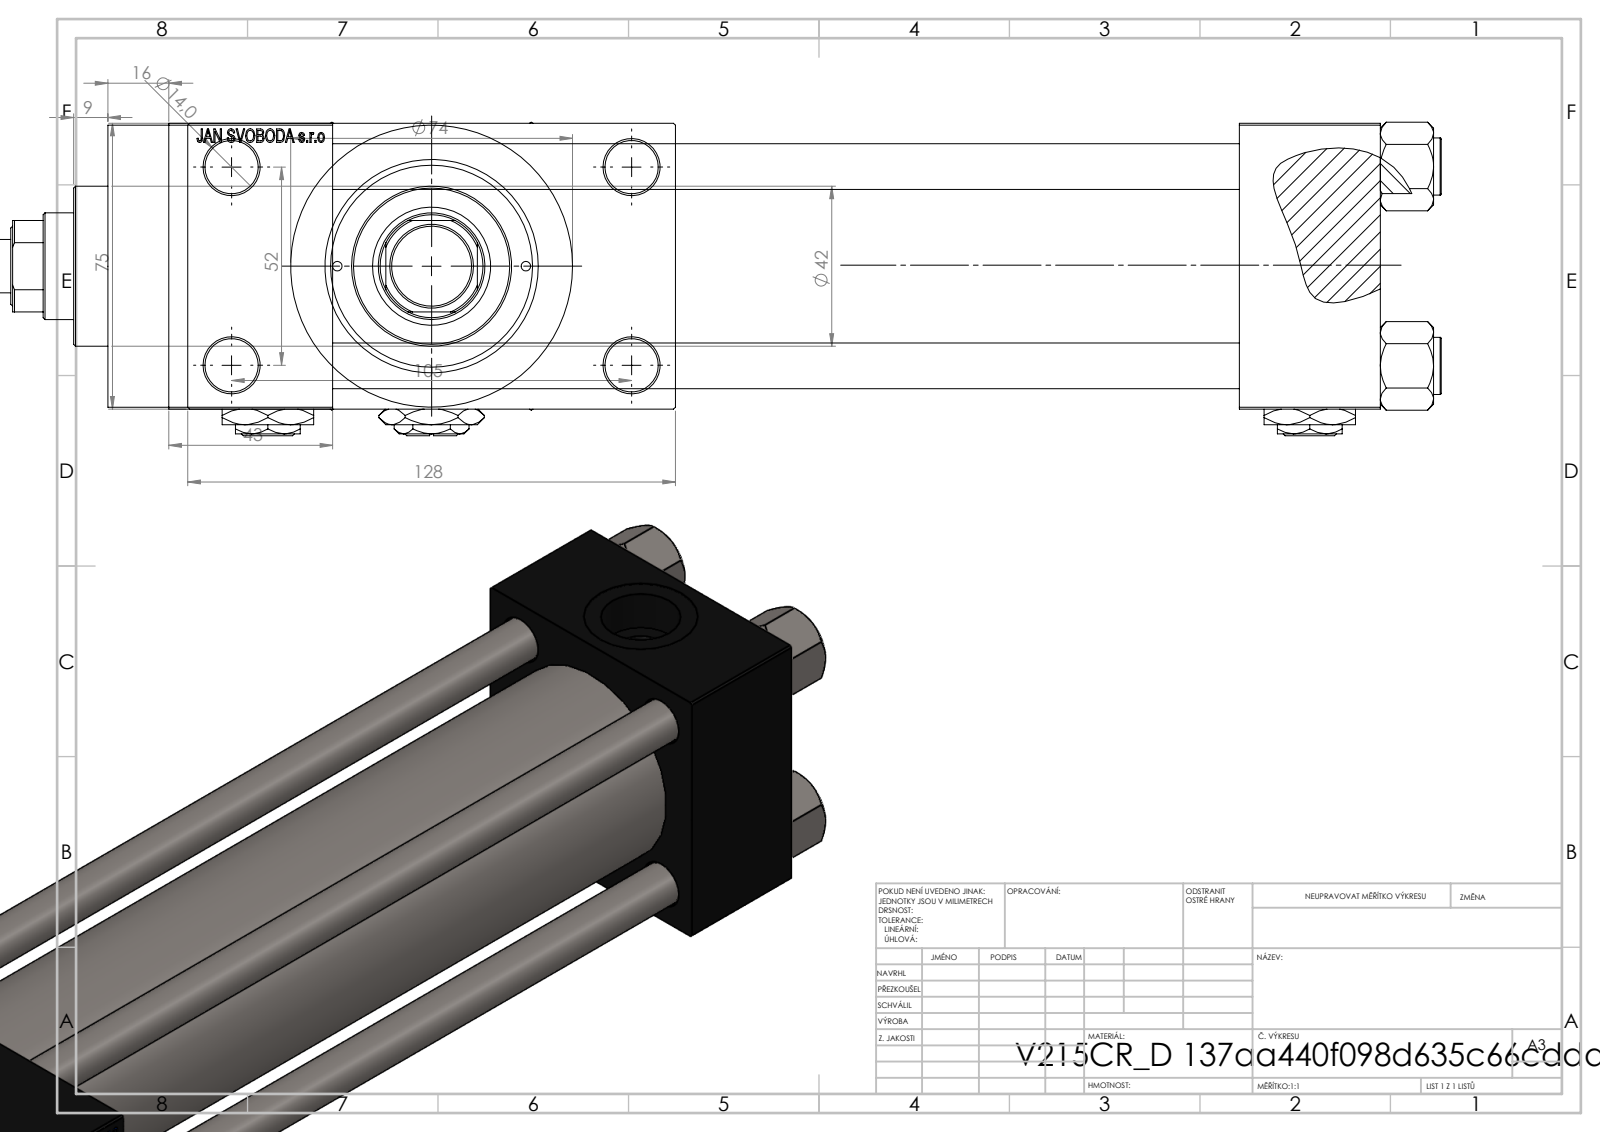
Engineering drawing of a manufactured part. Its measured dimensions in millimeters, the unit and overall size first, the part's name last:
Units: millimetres
Overall size (bounding box): 395 × 128 × 82.27
Round holes (diameter × count): ⌀12 ×4, ⌀14 ×4, ⌀2.5 ×2, ⌀7 ×2, ⌀20.96 ×2, ⌀30 ×2, ⌀18.5 ×1, ⌀28 ×1, ⌀31 ×1, ⌀41 ×1, ⌀50 ×1, ⌀53 ×1
Round bosses / shafts (diameter × count): ⌀15 ×4, ⌀74 ×1, ⌀56 ×1, ⌀42 ×1, ⌀22 ×1, ⌀14 ×1
Partial cylindrical surfaces — rounded edges, fillets, slot ends (radius × count): R13.5 ×1
Main face-to-face distances: 75, 238, 37, 275, 26.5, 101.5, 318, 281, 43, 16
Hole centre spacings: 26.19, 26.35, 36.98, 38.03, 52.3, 57.22, 58.43, 58.59
Volume: 1 098 000 mm³ · Surface area: 278 195 mm²
Bodies: 14 solids, 1227 faces (551 planar, 108 cylindrical, 568 other)
Part name (STEP PRODUCT): V215CR_D_Body; V215CR_ROD_END_W; V215CR_VCP_D; Zatka_pro_OIL_PORT (+3 more)
STEP written by: SolidWorks 2019 (CONFIG_CONTROL_DESIGN)
